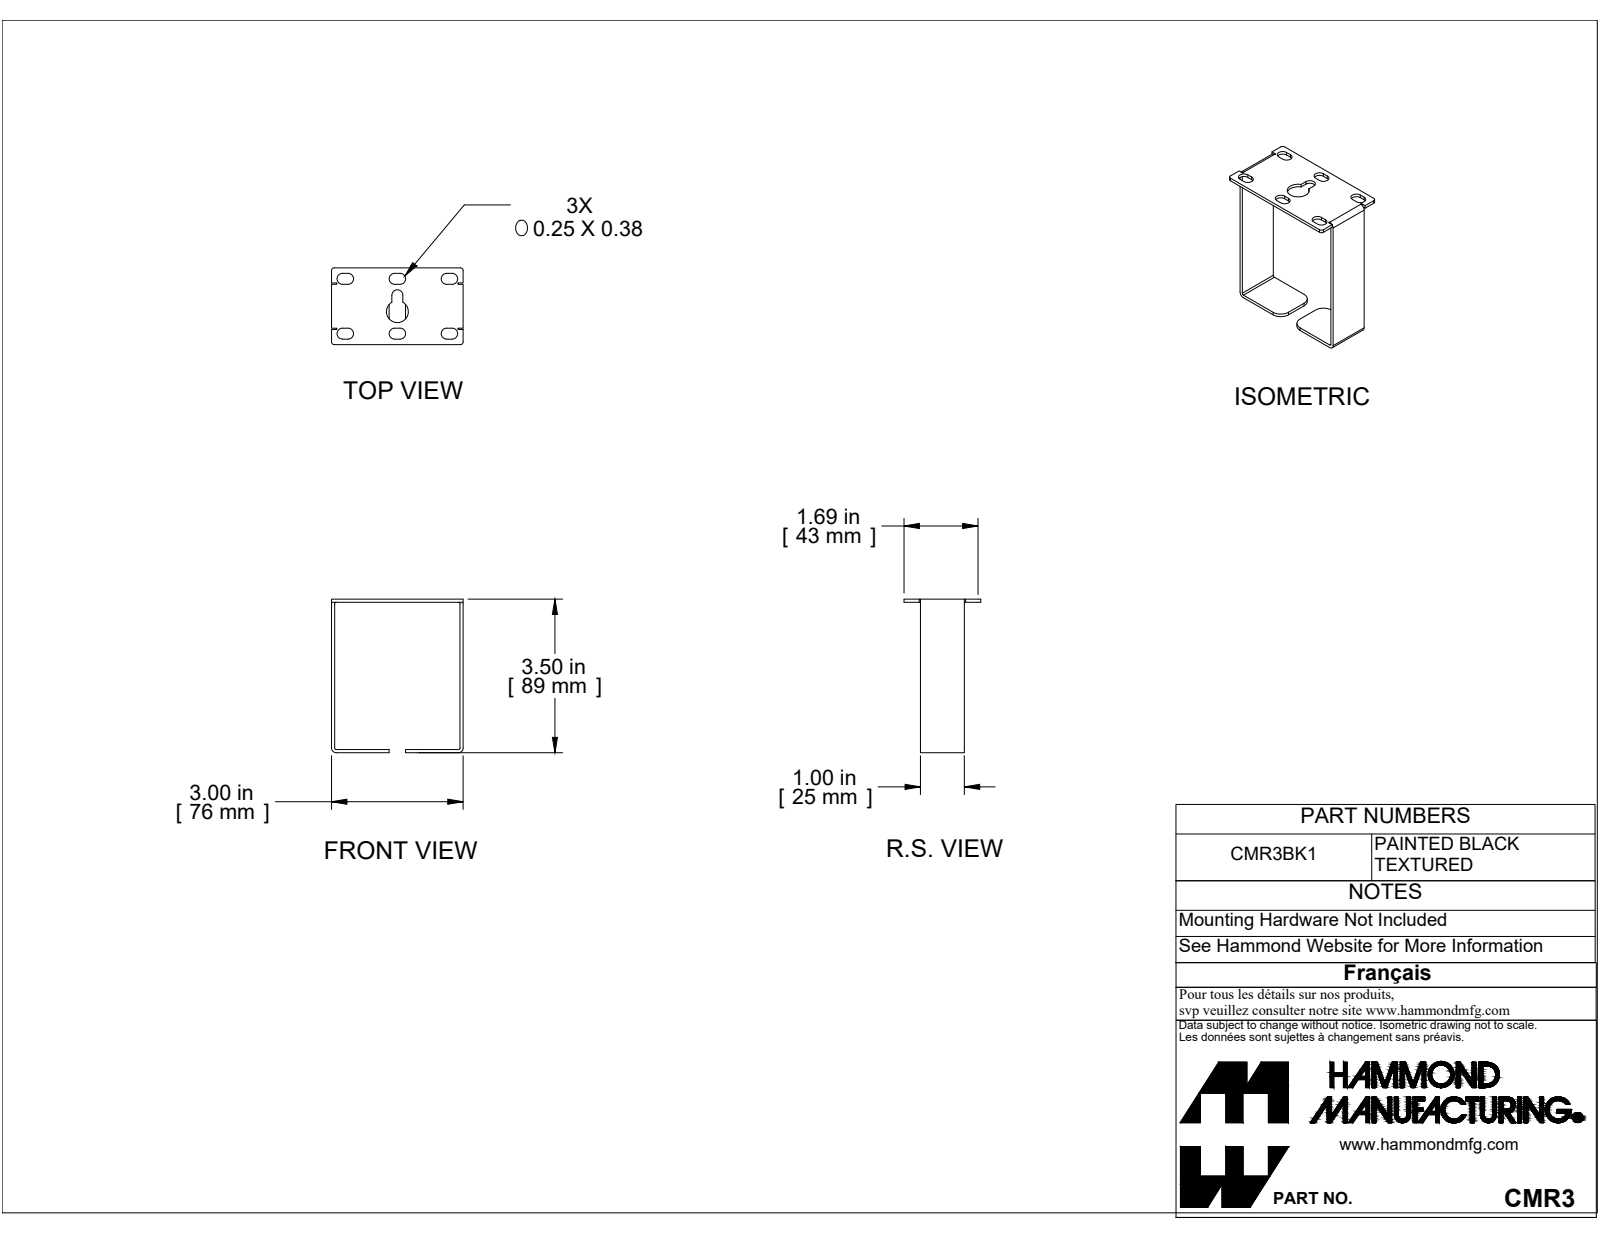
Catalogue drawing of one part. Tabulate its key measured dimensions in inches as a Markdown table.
| quantity | value |
| --- | --- |
| part name | CMR3BK1 |
| STEP written by | SolidWorks 2019 (AUTOMOTIVE_DESIGN) |
| units | inches |
| bodies | 1 solid, 74 faces (40 planar, 34 cylindrical, 0 other) |
| overall size | 3.5 × 3 × 1.75 |
| volume | 0.983 in³ |
| surface area | 29.94 in² |
| round holes (diameter × count) | 0.5 × 1 |
| partial cylindrical surfaces (radius × count) | 0.125 × 13, 0.015 × 4, 0.036 × 4, 0.062 × 4, 0.108 × 4, 0.25 × 4 |
| main face-to-face distances | 0.072, 2.928, 3.428, 3, 2.856, 3.5, 3.356, 1, 0.375, 1.375 |
